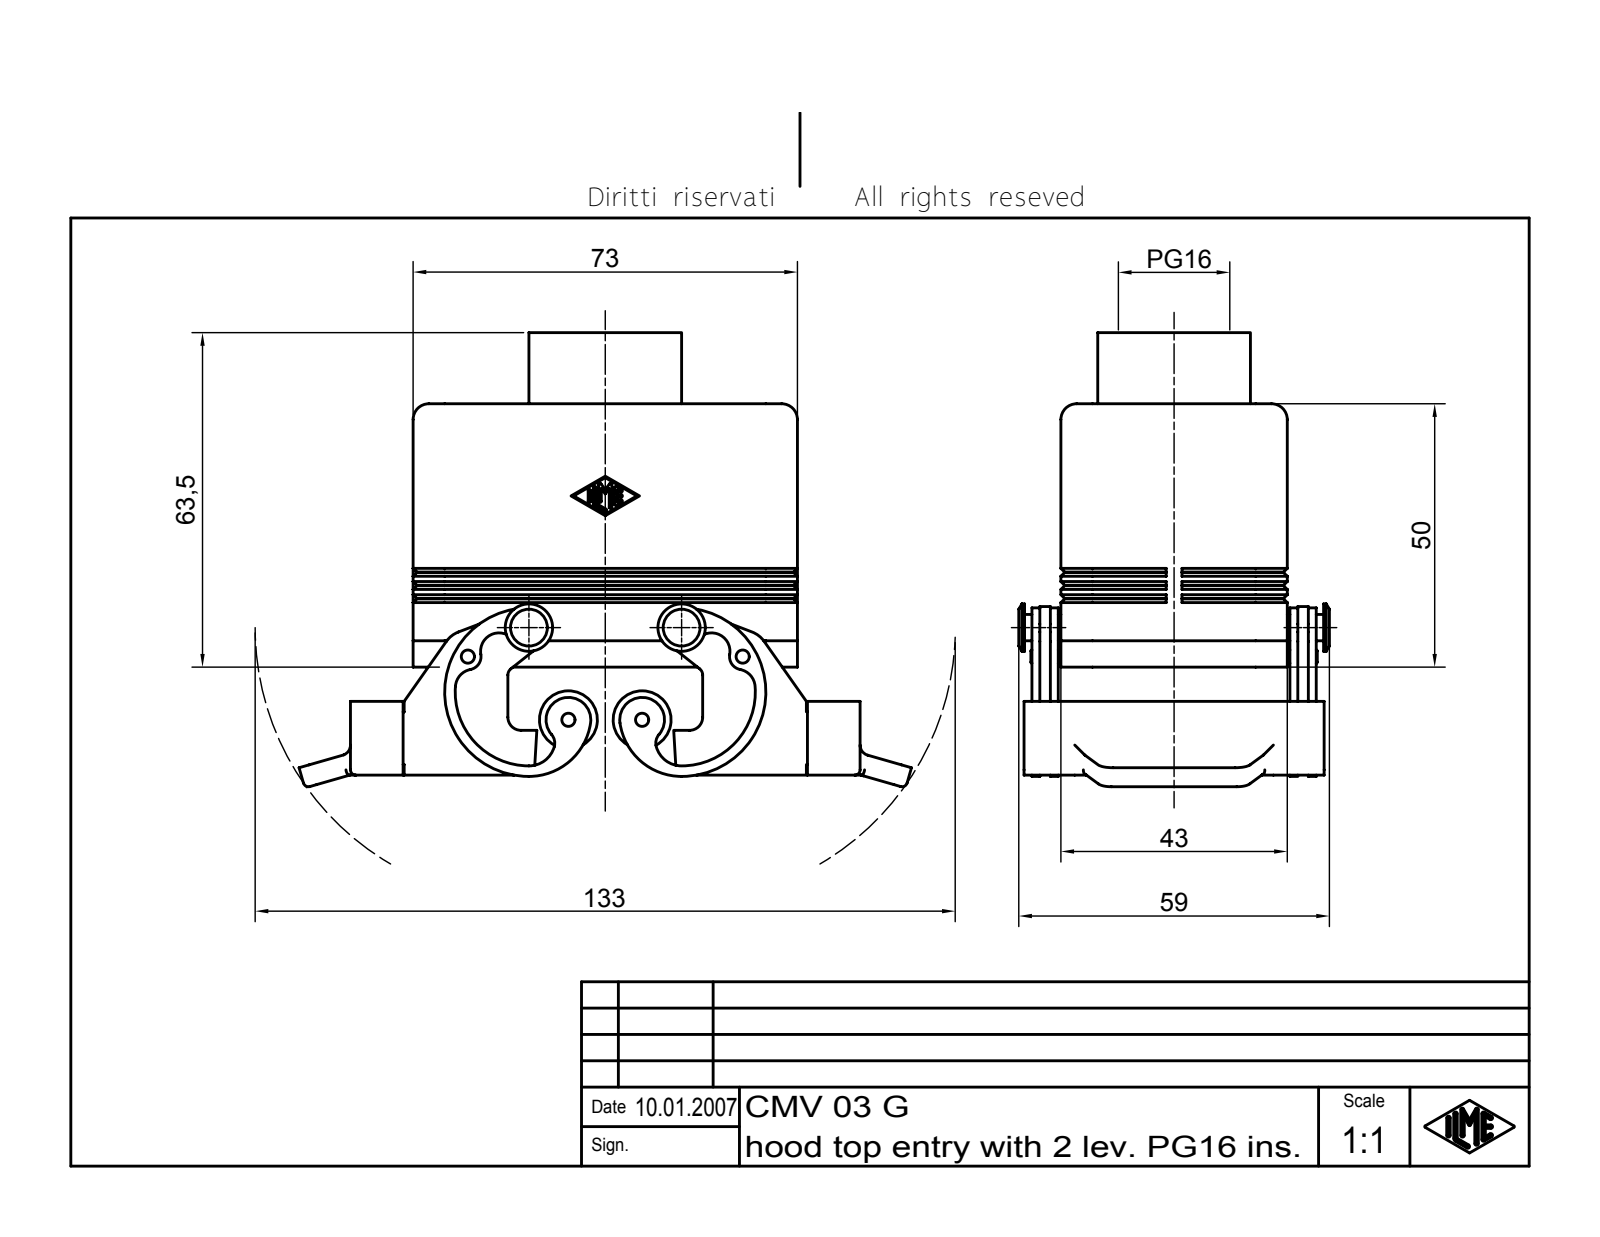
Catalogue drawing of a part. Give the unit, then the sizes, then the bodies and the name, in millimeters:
Units: millimetres
Overall size (bounding box): 116.32 × 86.21 × 59
Round holes (diameter × count): ⌀2.5 ×2, ⌀16 ×1, ⌀21.16 ×1
Round bosses / shafts (diameter × count): ⌀11 ×2, ⌀9 ×2, ⌀5 ×2, ⌀2 ×2, ⌀29 ×1
Partial cylindrical surfaces — rounded edges, fillets, slot ends (radius × count): R0.25 ×14, R3 ×12, R2 ×10, R1 ×8, R2.5 ×6, R3 ×4, R3.5 ×4, R5 ×4
Main face-to-face distances: 3, 40, 37, 8.5, 43, 47, 11.5, 70, 2, 5
Hole centre spacings: 52.2
Volume: 73 355 mm³ · Surface area: 45 752 mm²
Bodies: 1 solid, 771 faces (228 planar, 207 cylindrical, 336 other)
Part name (STEP PRODUCT): CHV Tüllengehäuse 2 Bügel für einen Einsatz
STEP written by: Autodesk Inventor 7 (AUTOMOTIVE_DESIGN)
